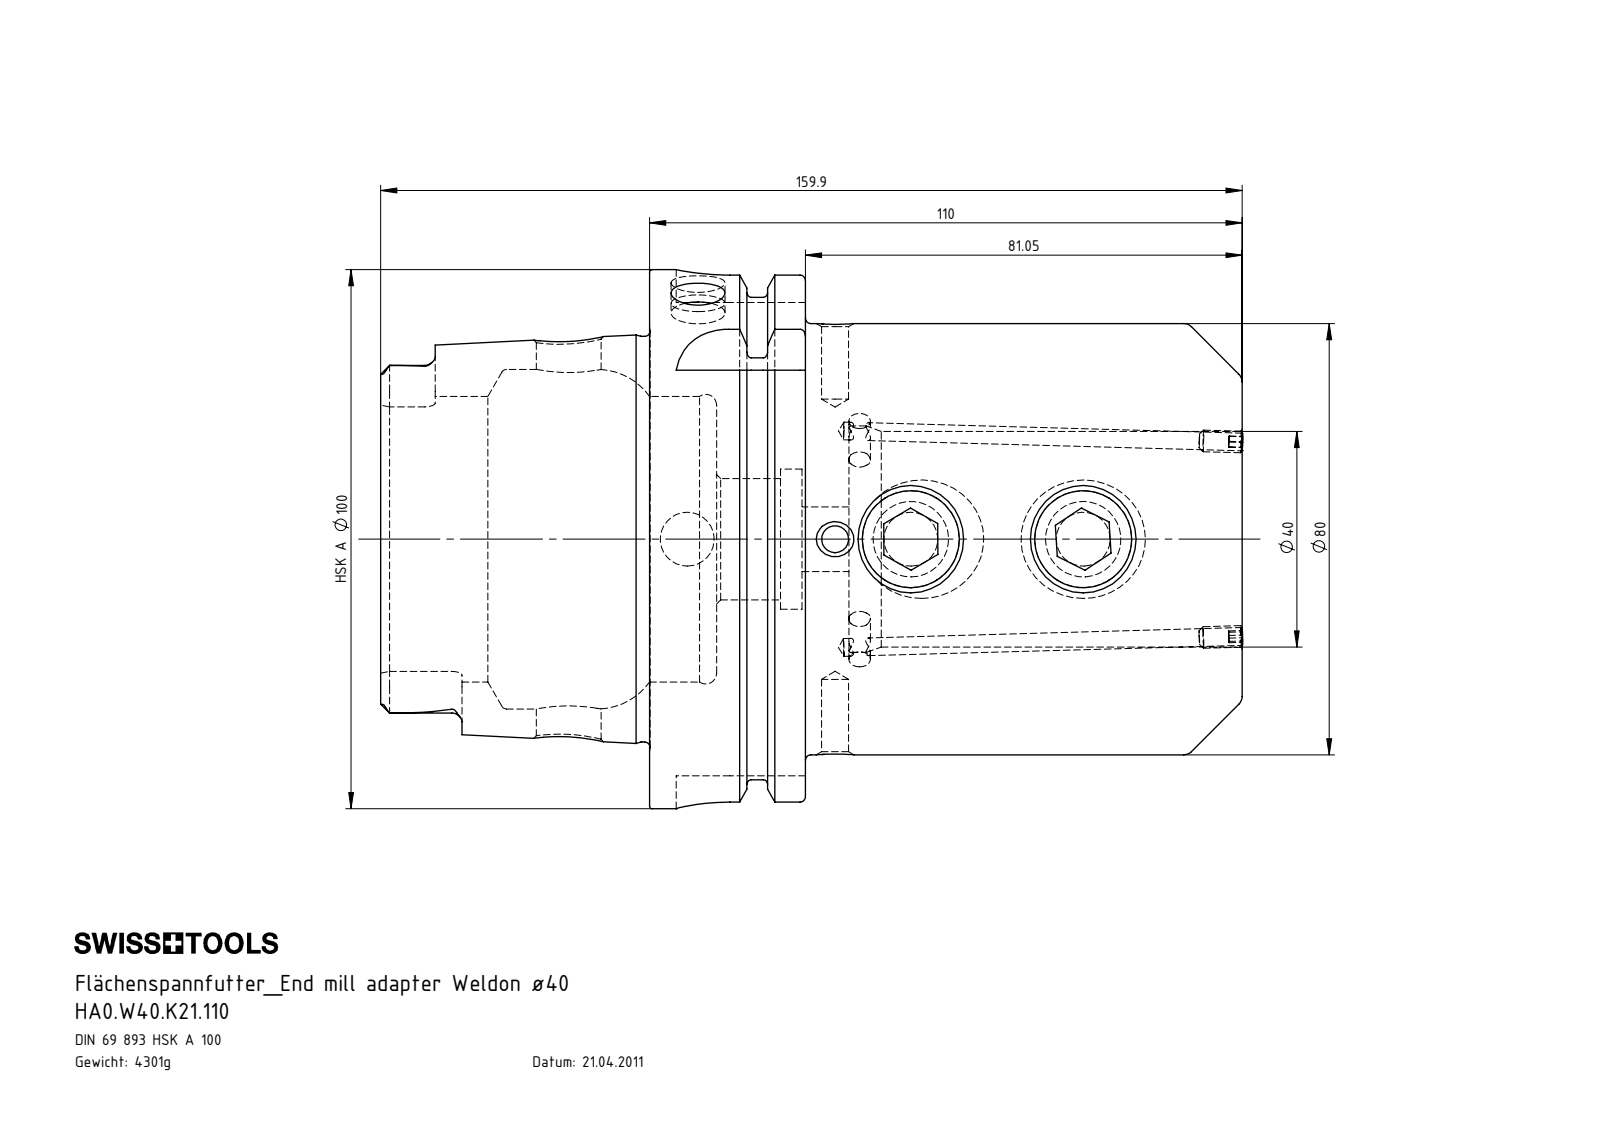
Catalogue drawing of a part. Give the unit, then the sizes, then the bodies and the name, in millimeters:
Units: millimetres
Overall size (bounding box): 160.01 × 100 × 100
Round holes (diameter × count): ⌀10 ×3, ⌀3.3 ×2, ⌀5 ×2, ⌀12 ×2, ⌀18 ×2, ⌀4 ×1, ⌀22.5 ×1, ⌀26 ×1, ⌀40 ×1, ⌀42 ×1, ⌀53 ×1, ⌀63 ×1
Round bosses / shafts (diameter × count): ⌀20 ×2, ⌀4 ×2, ⌀100 ×1, ⌀91.95 ×1, ⌀80 ×1, ⌀75.26 ×1
Partial cylindrical surfaces — rounded edges, fillets, slot ends (radius × count): R1.9 ×6, R4.88 ×4, R10 ×4
Main face-to-face distances: 28.95, 12.45, 16.5, 110, 97.55, 81.05, 37, 24.55, 8.05, 73
Hole centre spacings: 14.05, 27.45, 32, 41.5, 46.05, 49.45, 73.5
Volume: 547 861 mm³ · Surface area: 87 049 mm²
Bodies: 5 solids, 297 faces (81 planar, 87 cylindrical, 129 other)
Part name (STEP PRODUCT): HA0-W40.K21.110; ERU-CJ3.001.008; W40-ER1.001.020; HA0-W40.K21.110_B_Fertigbearbeitung
STEP written by: SolidWorks 2012 (CONFIG_CONTROL_DESIGN)
